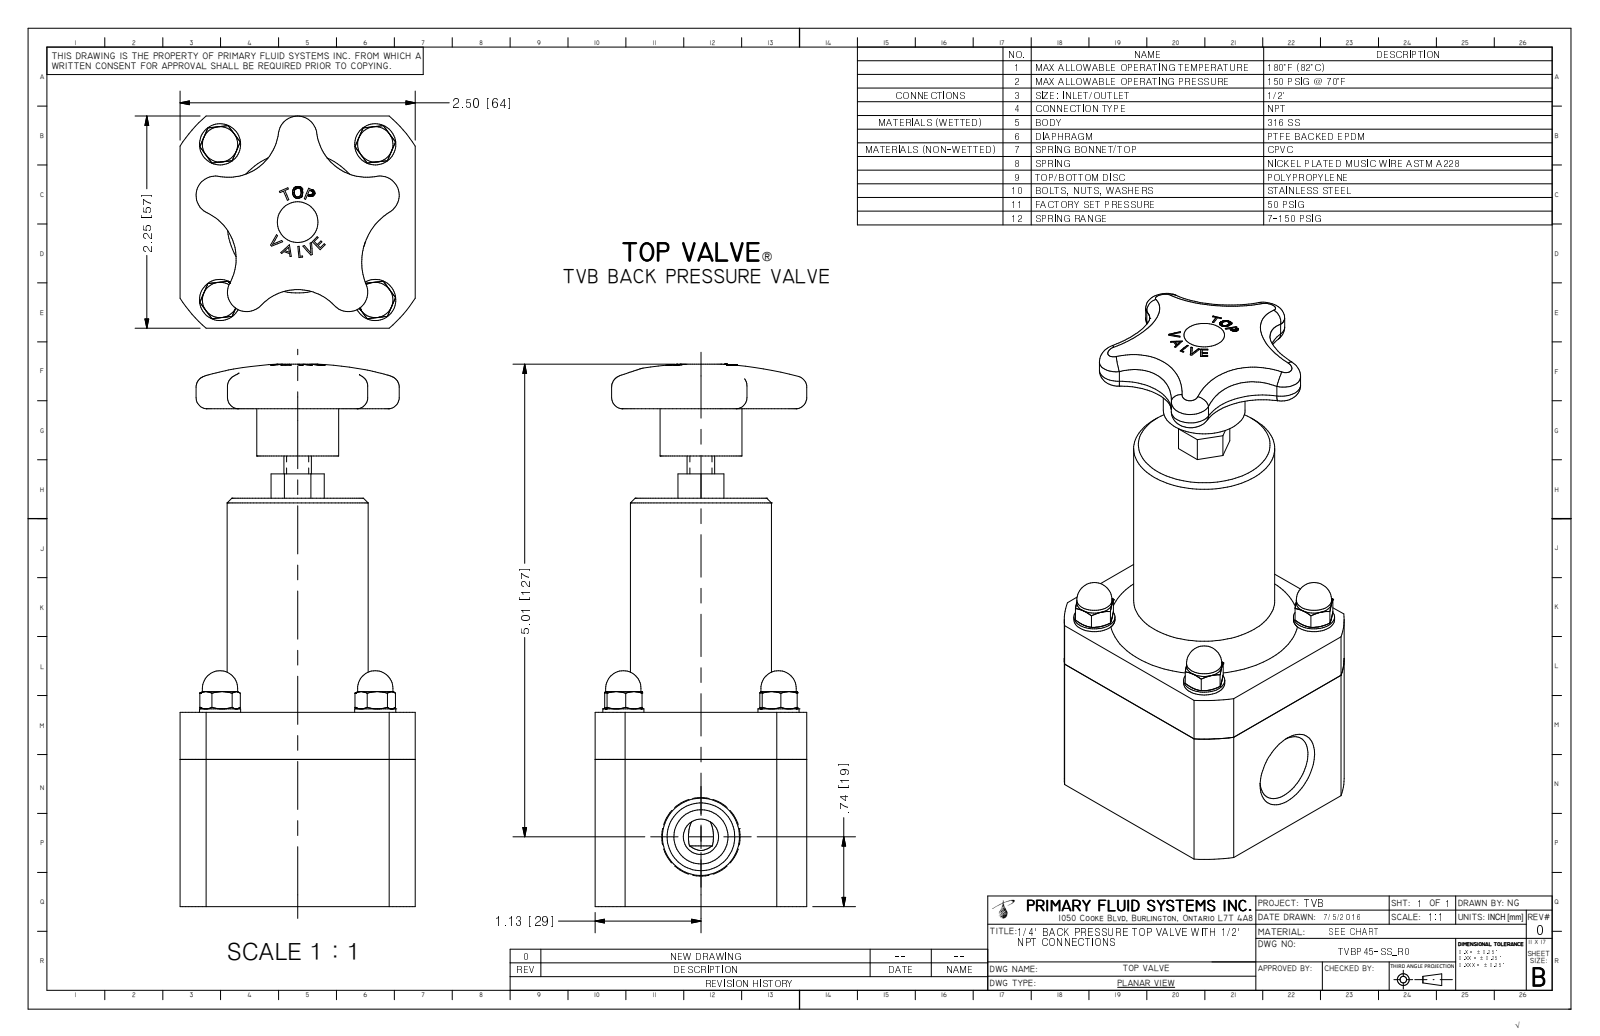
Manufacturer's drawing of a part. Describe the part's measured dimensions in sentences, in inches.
The part is named "TVBP45-SS-R0". Its 3-D file was written by "Autodesk Inventor 2009 (AUTOMOTIVE_DESIGN)". It is 1 solid with 337 faces: 140 planar, 45 cylindrical and 152 other. Overall it measures 5.752 by 2.5 by 2.25 inches. Its volume is 16.17 cubic inches and its surface area 56.21 square inches. Round holes: 4 of diameter 0.147, 1 of diameter 0.719. Round bosses or shafts: 4 of diameter 0.437, 4 of diameter 0.375, 4 of diameter 0.312, 1 of diameter 1.5, 1 of diameter 0.87, 1 of diameter 0.293. Partial cylindrical surfaces (rounded edges, fillets, slot ends): 5 of radius 0.085, 5 of radius 0.205, 4 of radius 0.536, 4 of radius 0.656, 1 of radius 0.625, 1 of radius 0.745, 1 of radius 1.488. The main face-to-face distances are 2.25, 2.5, 2.06, 4.33, 2.27, 0.6, 1.9, 4.778, 2.718, 0.448. The hole center spacings are 1.65, 1.65, 2.334.
